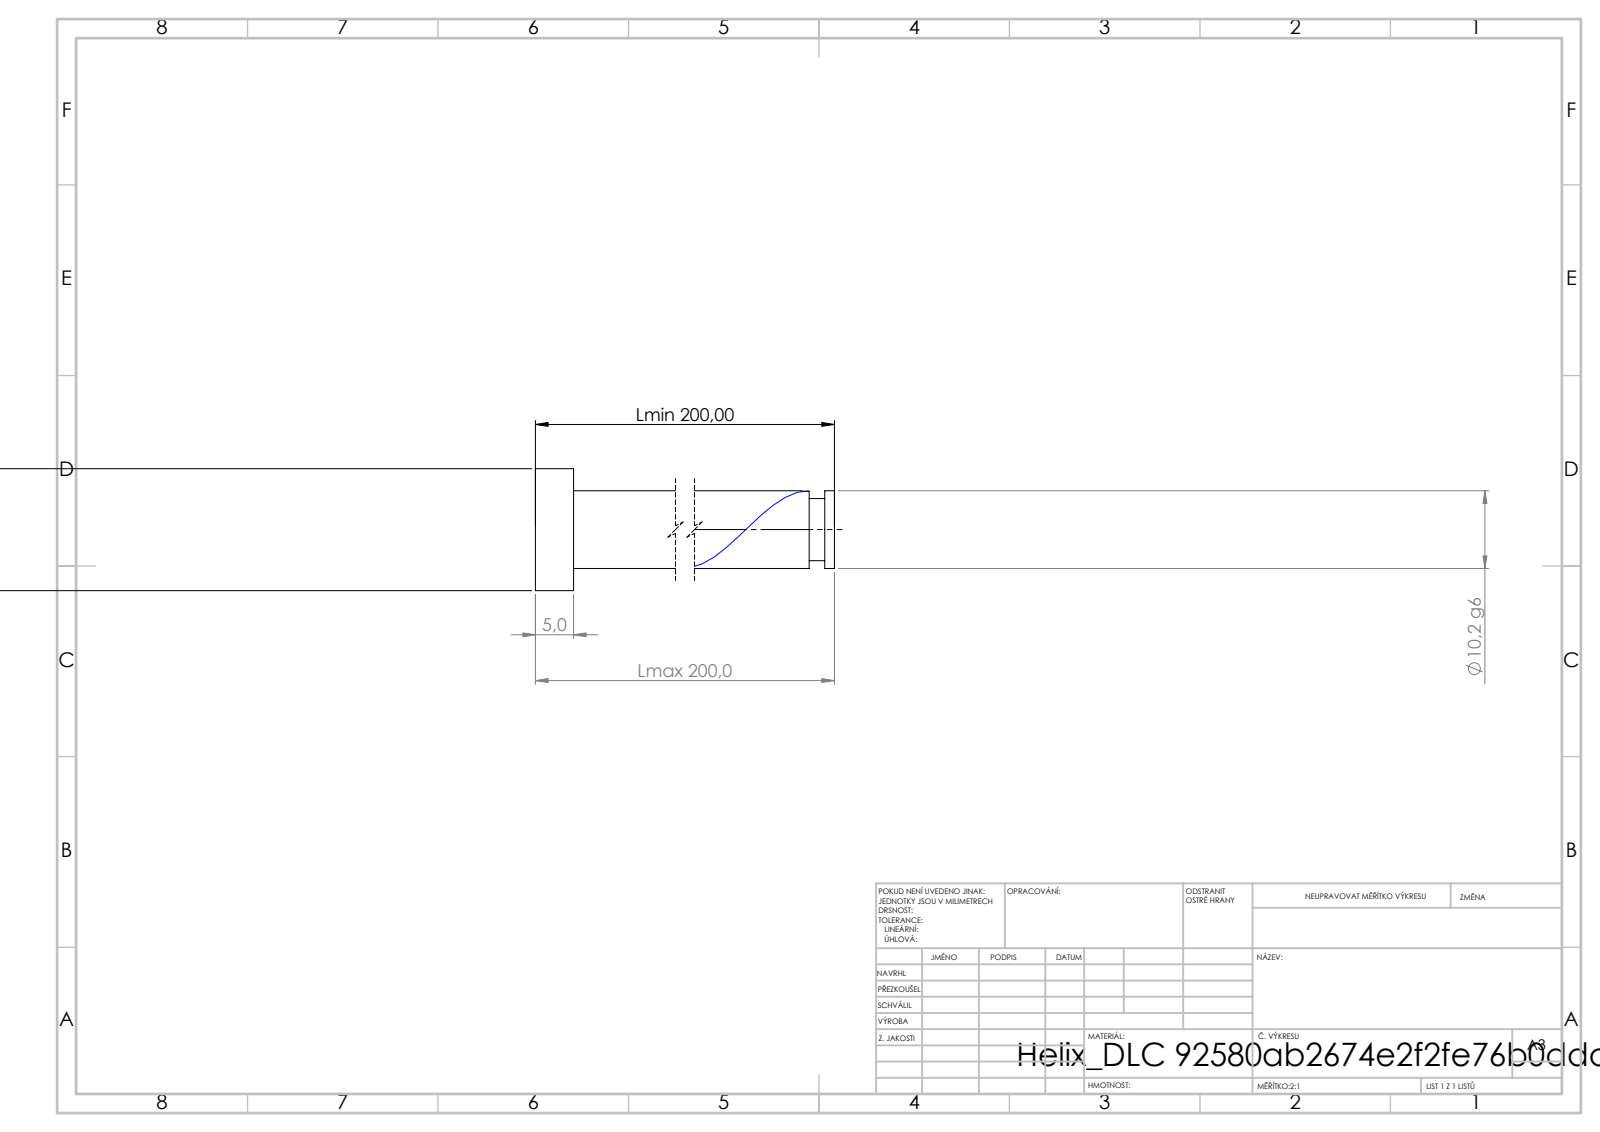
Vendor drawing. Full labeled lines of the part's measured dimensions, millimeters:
STEP written by: SolidWorks 2019 (CONFIG_CONTROL_DESIGN)
Units: millimetres
Bodies: 1 solid, 21 faces (6 planar, 14 cylindrical, 1 other)
Overall size (bounding box): 200 × 16 × 16
Volume: 16 723 mm³ · Surface area: 7 100 mm²
Round bosses / shafts (diameter × count): ⌀16 ×1, ⌀10.2 ×1, ⌀8.16 ×1
Main face-to-face distances: 5, 200, 195, 198.73, 193.73, 1.27, 196.69, 191.69, 2.04, 3.31
